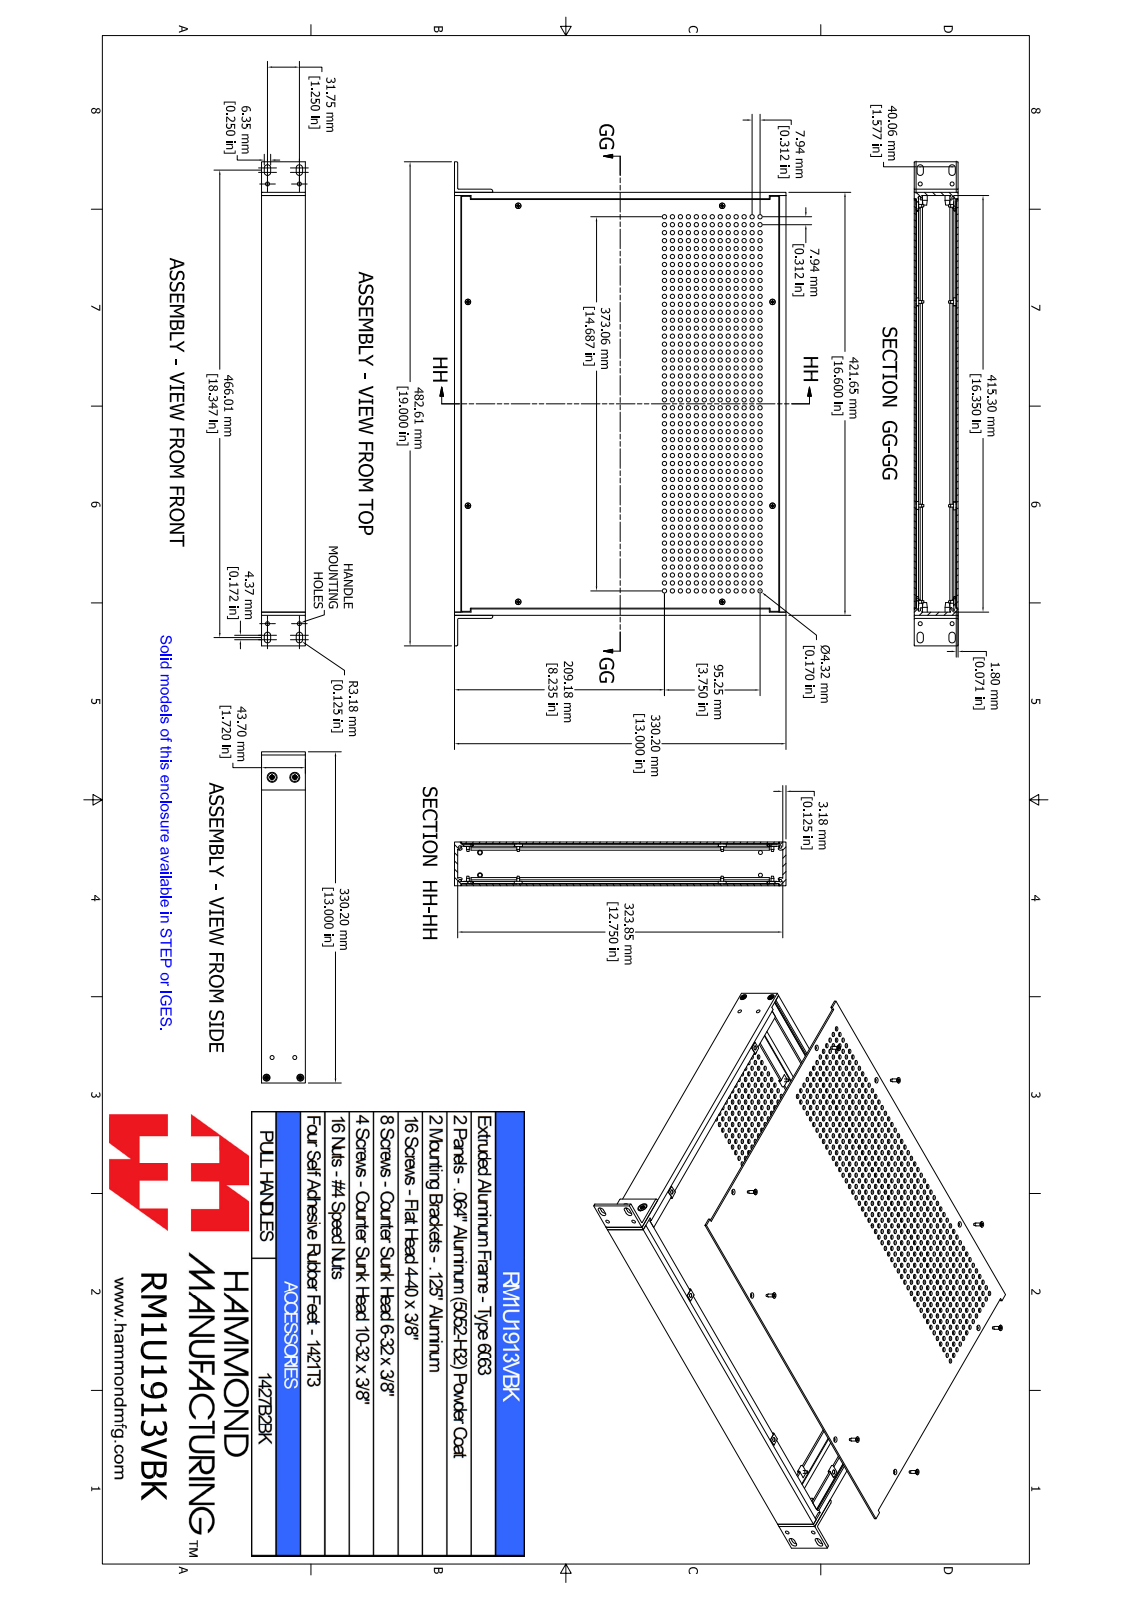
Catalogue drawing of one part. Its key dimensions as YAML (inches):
part_name: "RM1U1913VBK"
step_written_by: "SolidWorks 2021 (AUTOMOTIVE_DESIGN)"
units: inches
bodies: {solids: 52, faces: 2600, planar: 636, cylindrical: 1468, other: 496}
overall_size: [19, 13, 1.72]
volume: 47.74
surface_area: 1202
round_holes:
  - {diameter: 0.17, count: 624}
  - {diameter: 0.098, count: 8}
  - {diameter: 0.118, count: 8}
  - {diameter: 0.157, count: 8}
  - {diameter: 0.169, count: 8}
  - {diameter: 0.138, count: 4}
  - {diameter: 0.156, count: 4}
  - {diameter: 0.157, count: 4}
  - {diameter: 0.197, count: 2}
round_bosses_or_shafts:
  - {diameter: 0.214, count: 8}
  - {diameter: 0.112, count: 8}
  - {diameter: 0.238, count: 4}
  - {diameter: 0.138, count: 4}
  - {diameter: 0.333, count: 2}
  - {diameter: 0.19, count: 2}
partial_cylinders:
  - {radius: 0.039, count: 20}
  - {radius: 0.125, count: 16}
  - {radius: 0.049, count: 14}
  - {radius: 0.05, count: 8}
  - {radius: 0.038, count: 6}
  - {radius: 0.037, count: 4}
  - {radius: 0.079, count: 2}
face_to_face_distances: [0.071, 1.649, 1.72, 1.578, 1.482, 0.167, 1.553, 0.096, 0.125, 0.125]
hole_center_spacings: [1.25, 0.313, 0.937, 2.5, 1.563, 2.187, 0.625, 0.625]
